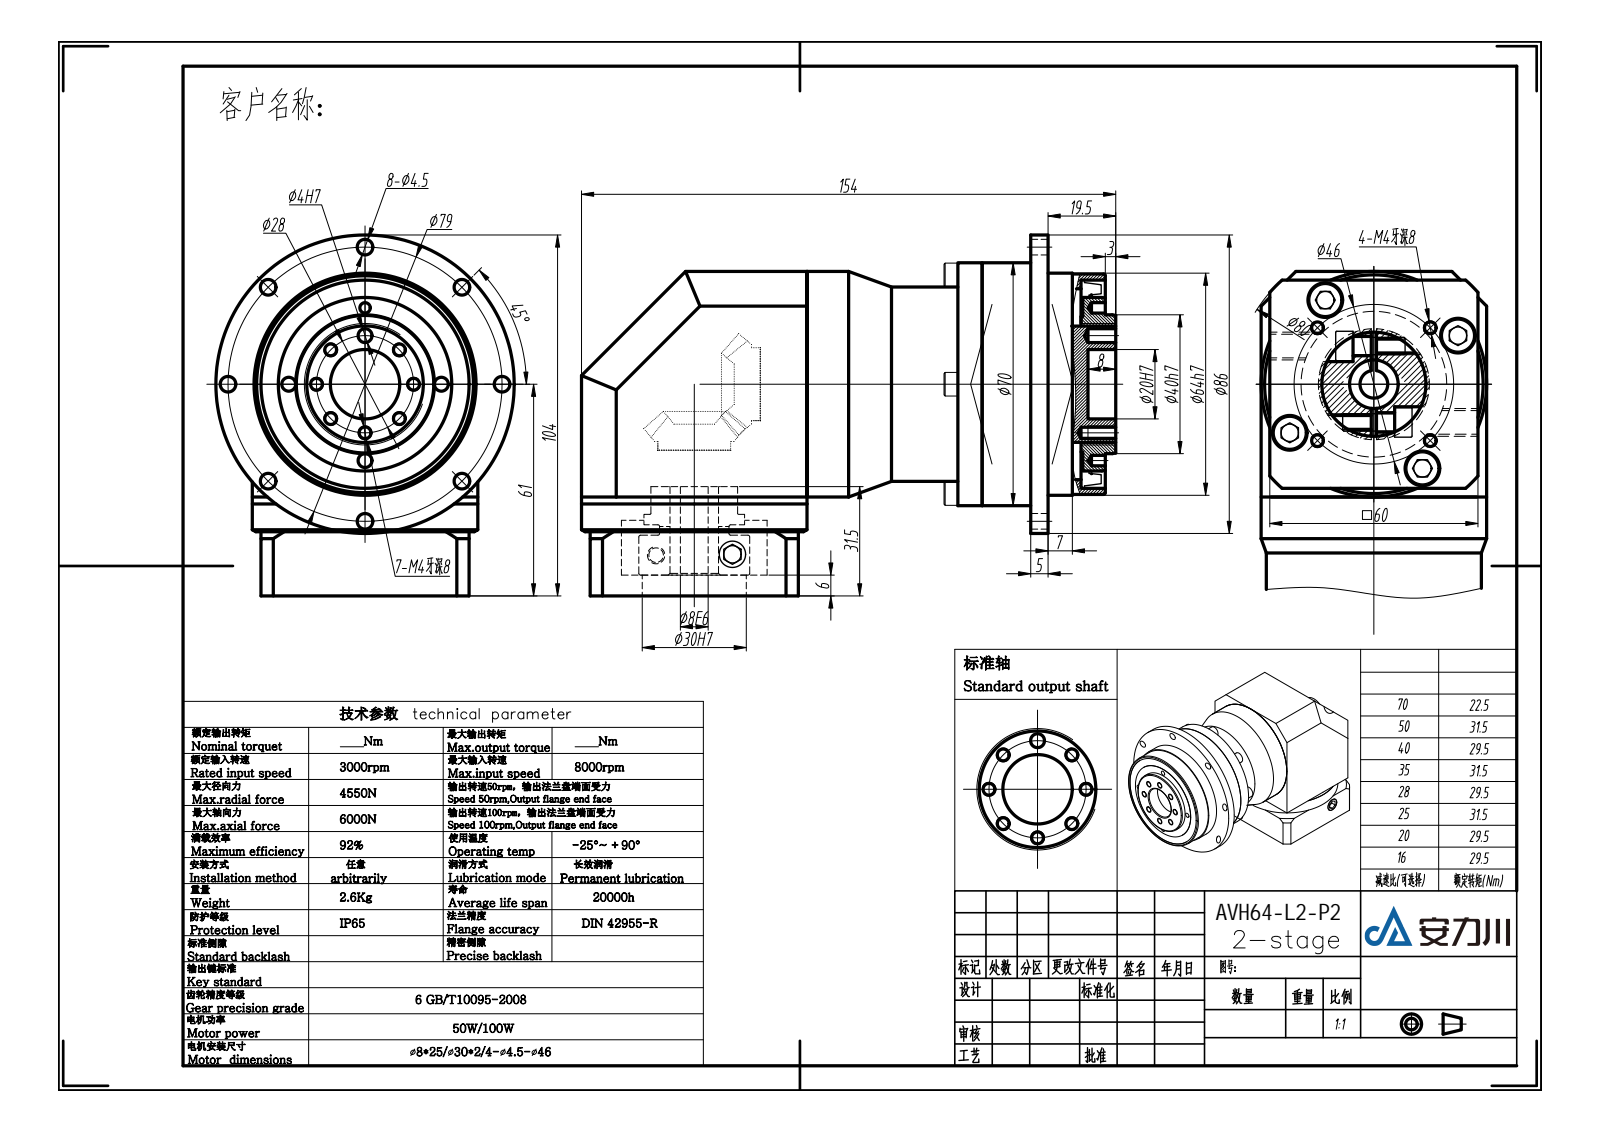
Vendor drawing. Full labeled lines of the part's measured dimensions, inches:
Part name (STEP PRODUCT): VGZH64双级模型（8-25 30-3 4-4.5-46）
STEP written by: SolidWorks 2016 (AUTOMOTIVE_DESIGN)
Units: inches
Bodies: 5 solids, 441 faces (231 planar, 158 cylindrical, 52 other)
Overall size (bounding box): 6.063 × 4.094 × 3.386
Volume: 36.23 in³ · Surface area: 131.6 in²
Round holes (diameter × count): ⌀0.13 ×11, ⌀0.177 ×8, ⌀0.118 ×4, ⌀0.374 ×4, ⌀0.394 ×4, ⌀0.315 ×3, ⌀0.787 ×2, ⌀0.157 ×1, ⌀0.551 ×1, ⌀1.181 ×1, ⌀1.654 ×1, ⌀2.362 ×1
Round bosses / shafts (diameter × count): ⌀0.335 ×8, ⌀0.268 ×8, ⌀2.559 ×2, ⌀0.307 ×2, ⌀3.386 ×1, ⌀2.756 ×1, ⌀2.52 ×1, ⌀2.5 ×1
Partial cylindrical surfaces — rounded edges, fillets, slot ends (radius × count): R1.575 ×1
Main face-to-face distances: 2.559, 0.098, 2.461, 0.197, 1.043, 2.638, 0.236, 0.748, 0.807, 0.551
Hole centre spacings: 1.229, 1.65, 1.983, 0.551, 1.102, 0.422, 0.6, 0.78
